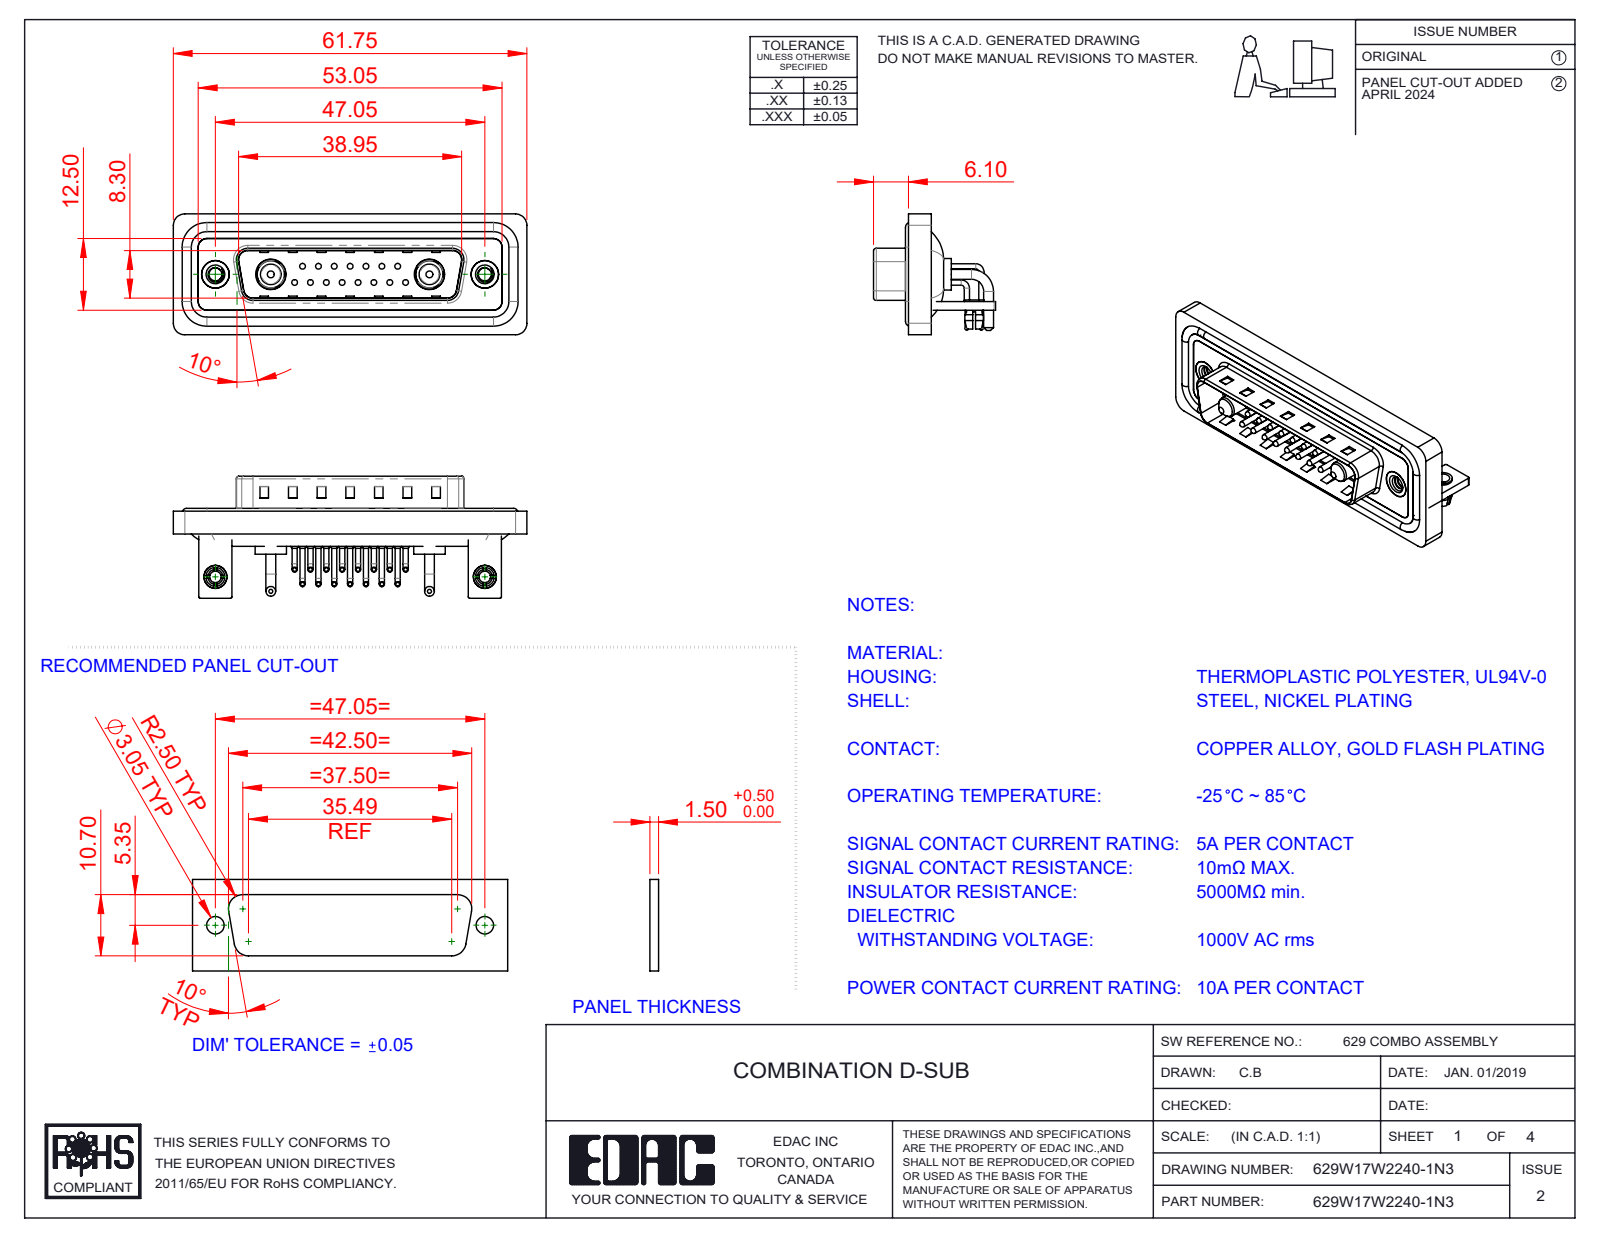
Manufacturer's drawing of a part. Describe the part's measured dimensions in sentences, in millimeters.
The part is named "Power Pin_10A RA; 629Combo Waterproof Housing_25 Contacts; 629Combo Shell Front_25 Contacts; 629Combo Contact Row 1 (+7 more)". Its 3-D file was written by "SolidWorks 2023 (CONFIG_CONTROL_DESIGN)". It is 30 solids with 2351 faces: 1257 planar, 820 cylindrical and 274 other. Overall it measures 61.75 by 21.3 by 21.1 millimeters. Its volume is 7 710 cubic millimeters and its surface area 13 296 square millimeters. Round holes: 17 of diameter 2, 15 of diameter 0.75, 15 of diameter 1.6, 2 of diameter 2.26, 2 of diameter 2.5, 2 of diameter 3.2, 2 of diameter 4, 2 of diameter 4.8, 2 of diameter 4.85, 2 of diameter 5, 2 of diameter 5.3. Round bosses or shafts: 30 of diameter 0.9, 15 of diameter 1.5, 15 of diameter 1, 15 of diameter 0.65, 4 of diameter 1.7, 4 of diameter 1.6, 2 of diameter 5.5, 2 of diameter 5.2. Partial cylindrical surfaces (rounded edges, fillets, slot ends): 19 of radius 2, 18 of radius 1.5, 16 of radius 0.25, 15 of radius 1.01, 9 of radius 0.5, 8 of radius 1.6, 4 of radius 0.6, 4 of radius 0.65. The main face-to-face distances are 0.4, 0.8, 1.5, 2.1, 2.9, 1.1, 4.1, 1.6, 4.5, 3.7. The hole center spacings are 3.16, 2.77, 5.54, 8.31, 5.04, 7.49, 11.08, 5.03.
